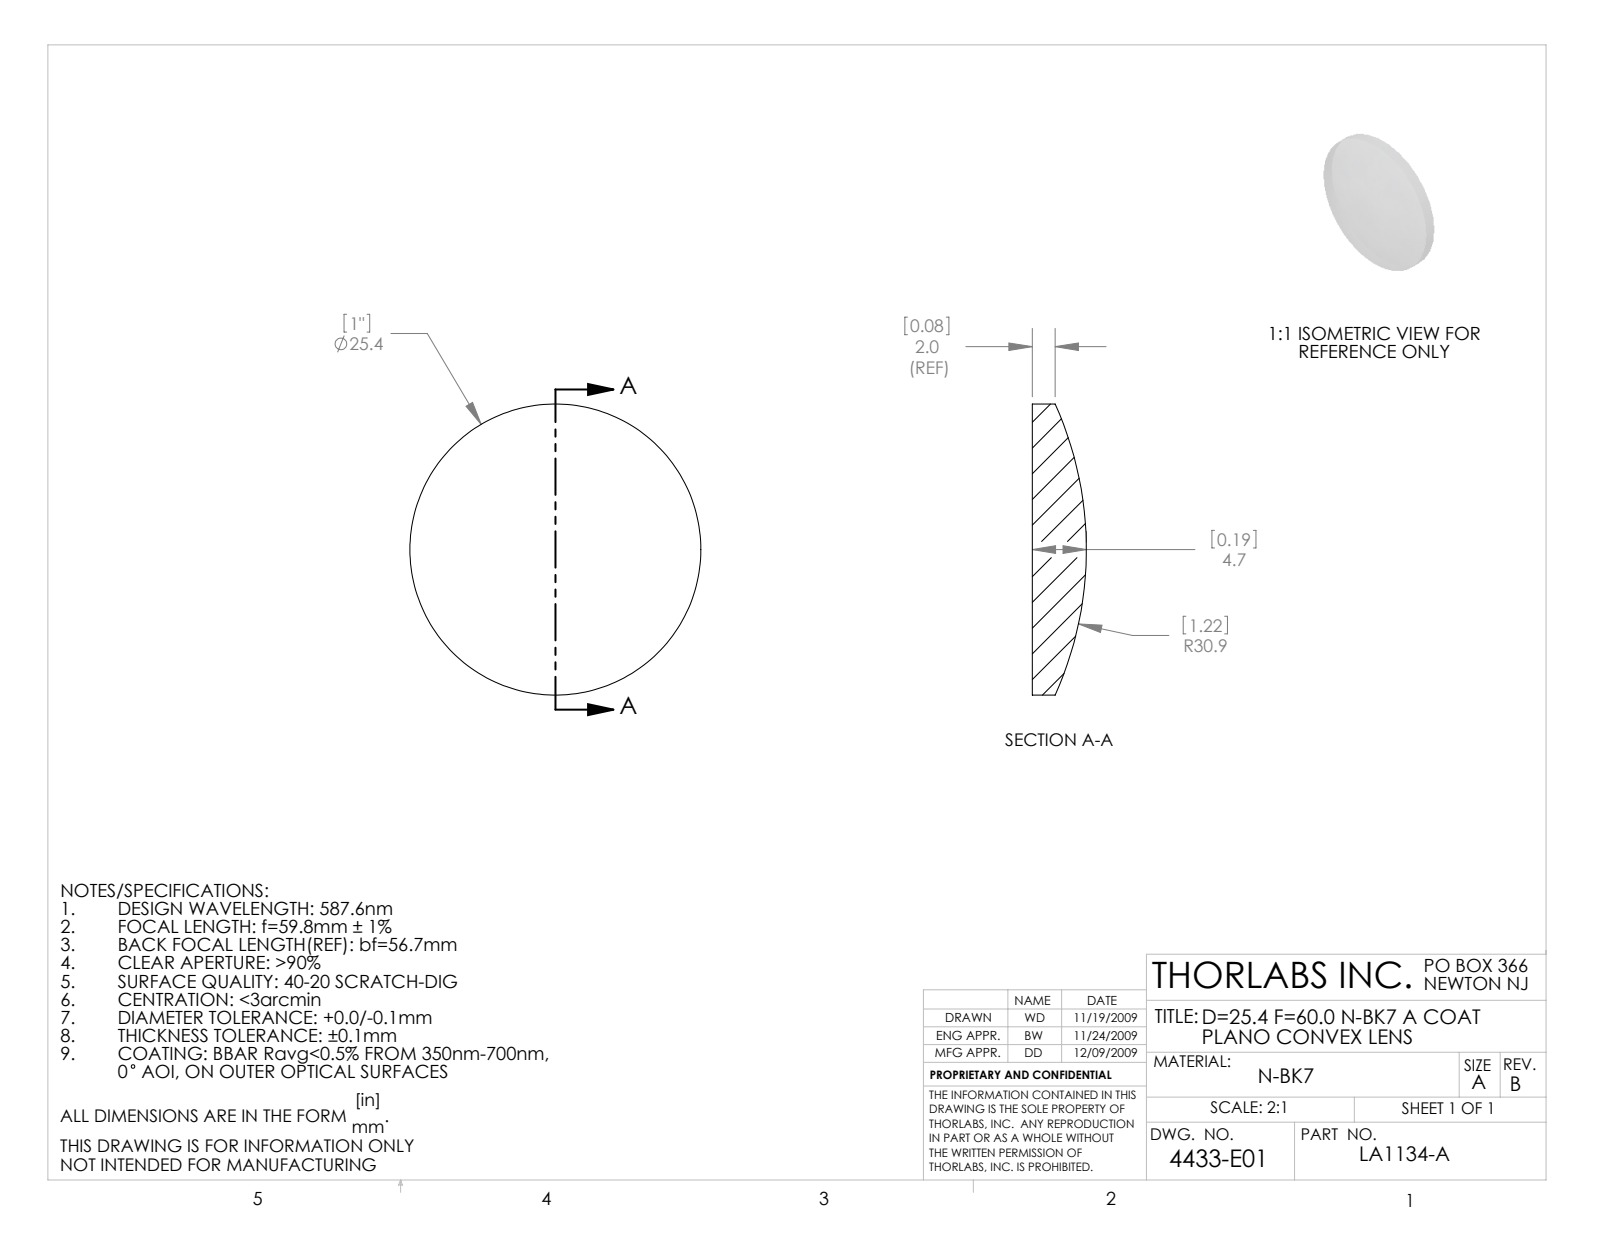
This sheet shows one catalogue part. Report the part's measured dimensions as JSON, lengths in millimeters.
{"part_name": "4433-E0W", "step_written_by": "SolidWorks 2009 (AUTOMOTIVE_DESIGN)", "units": "millimeters", "bodies": {"solids": 1, "faces": 5, "planar": 1, "cylindrical": 2, "other": 2}, "overall_size": [25.4, 25.4, 4.73], "volume_mm3": 1716, "surface_area_mm2": 1196, "round_bosses_or_shafts": [[25.4, 1]]}
